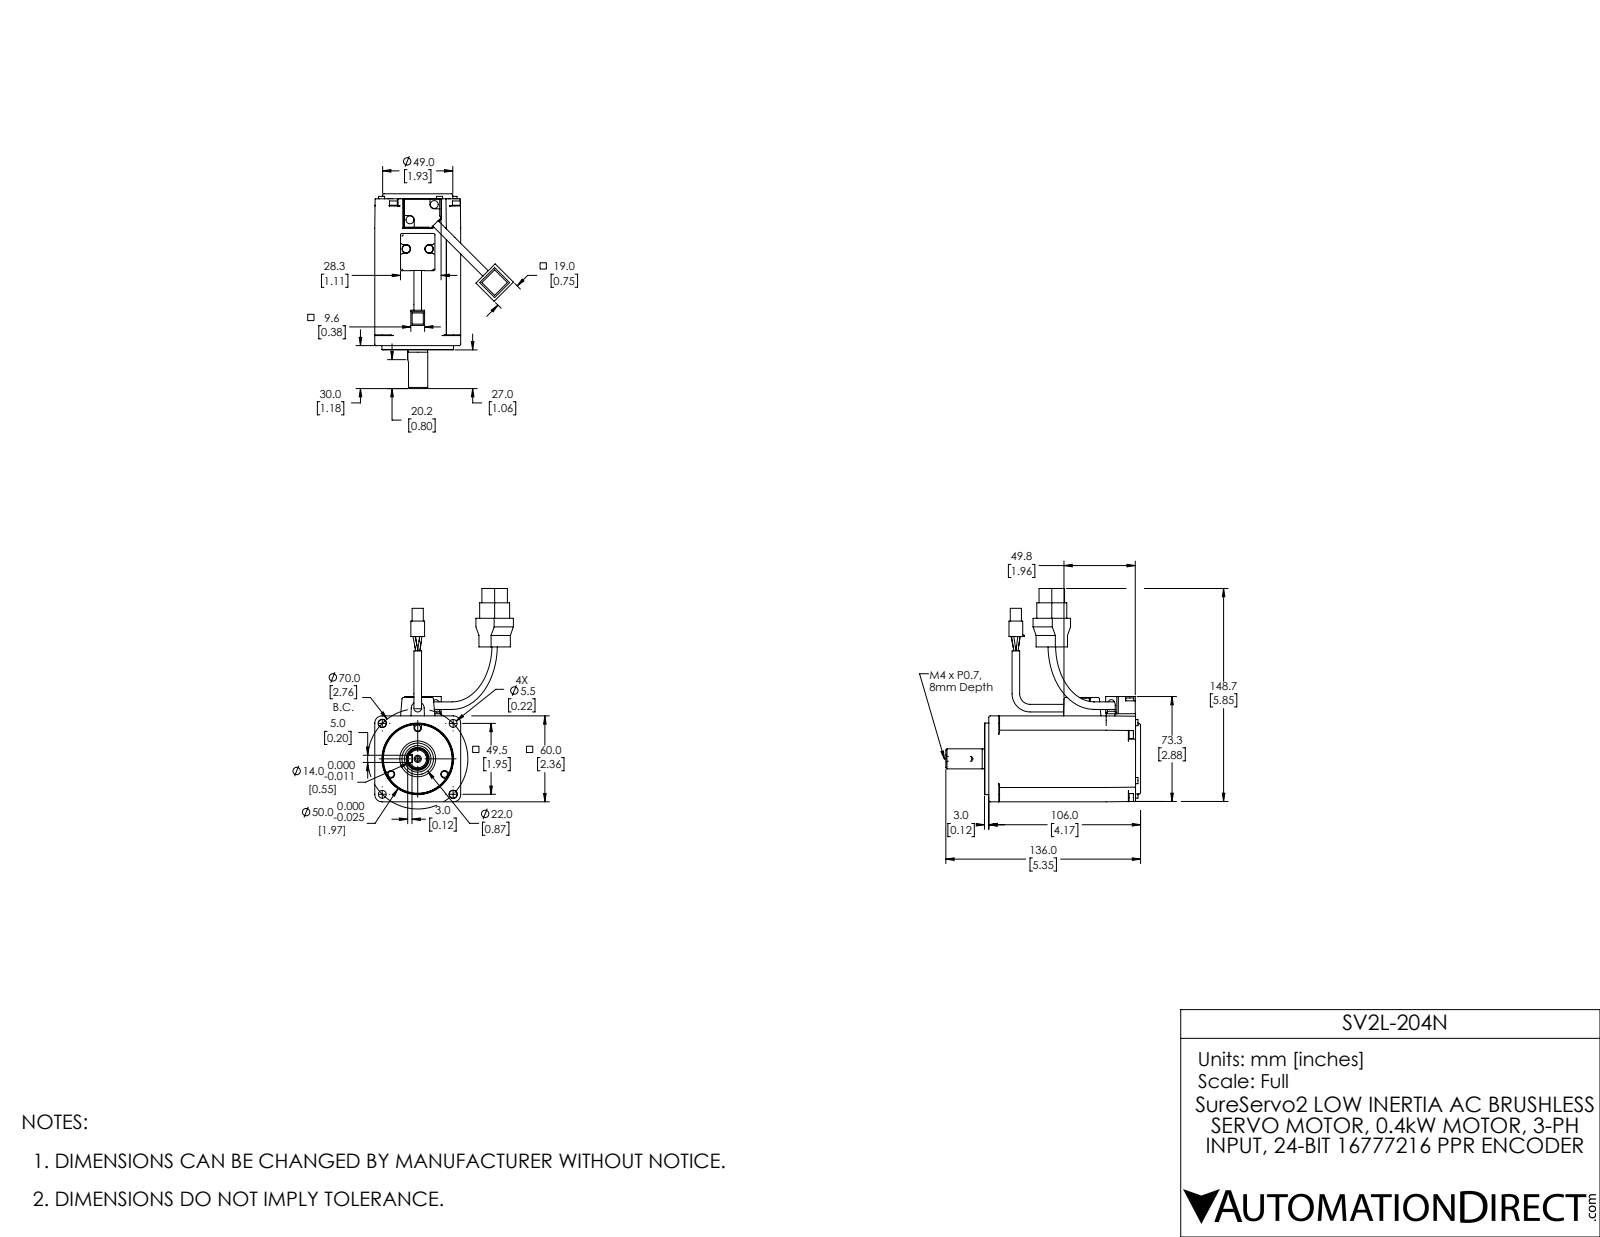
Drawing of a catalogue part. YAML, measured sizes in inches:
part_name: "ECM-A3H-CX0604RSX P1 Coord fXT"
step_written_by: "SolidWorks 2017 (AUTOMOTIVE_DESIGN)"
units: inches
bodies: {solids: 1, faces: 608, planar: 199, cylindrical: 215, other: 194}
overall_size: [5.863, 5.354, 3.811]
volume: 22.65
surface_area: 67.59
round_holes:
  - {diameter: 0.13, count: 4}
  - {diameter: 0.217, count: 2}
  - {diameter: 0.236, count: 1}
  - {diameter: 0.63, count: 1}
  - {diameter: 0.866, count: 1}
  - {diameter: 0.984, count: 1}
  - {diameter: 1.89, count: 1}
round_bosses_or_shafts:
  - {diameter: 0.217, count: 8}
  - {diameter: 0.169, count: 7}
  - {diameter: 0.228, count: 6}
  - {diameter: 0.209, count: 4}
  - {diameter: 0.059, count: 4}
  - {diameter: 0.118, count: 3}
  - {diameter: 1.969, count: 1}
  - {diameter: 1.929, count: 1}
partial_cylinders:
  - {radius: 0.039, count: 20}
  - {radius: 0.079, count: 16}
  - {radius: 0.006, count: 12}
  - {radius: 0.012, count: 12}
  - {radius: 0.118, count: 10}
  - {radius: 0.02, count: 8}
  - {radius: 0.087, count: 6}
  - {radius: 0.197, count: 4}
face_to_face_distances: [2.362, 0.394, 0.098, 4.272, 4.173, 1.969, 0.138, 4.134, 4.035, 0.539]
hole_center_spacings: [1.378, 0.791, 1.256, 1.646, 2.06, 2.713, 2.756, 2.898]
